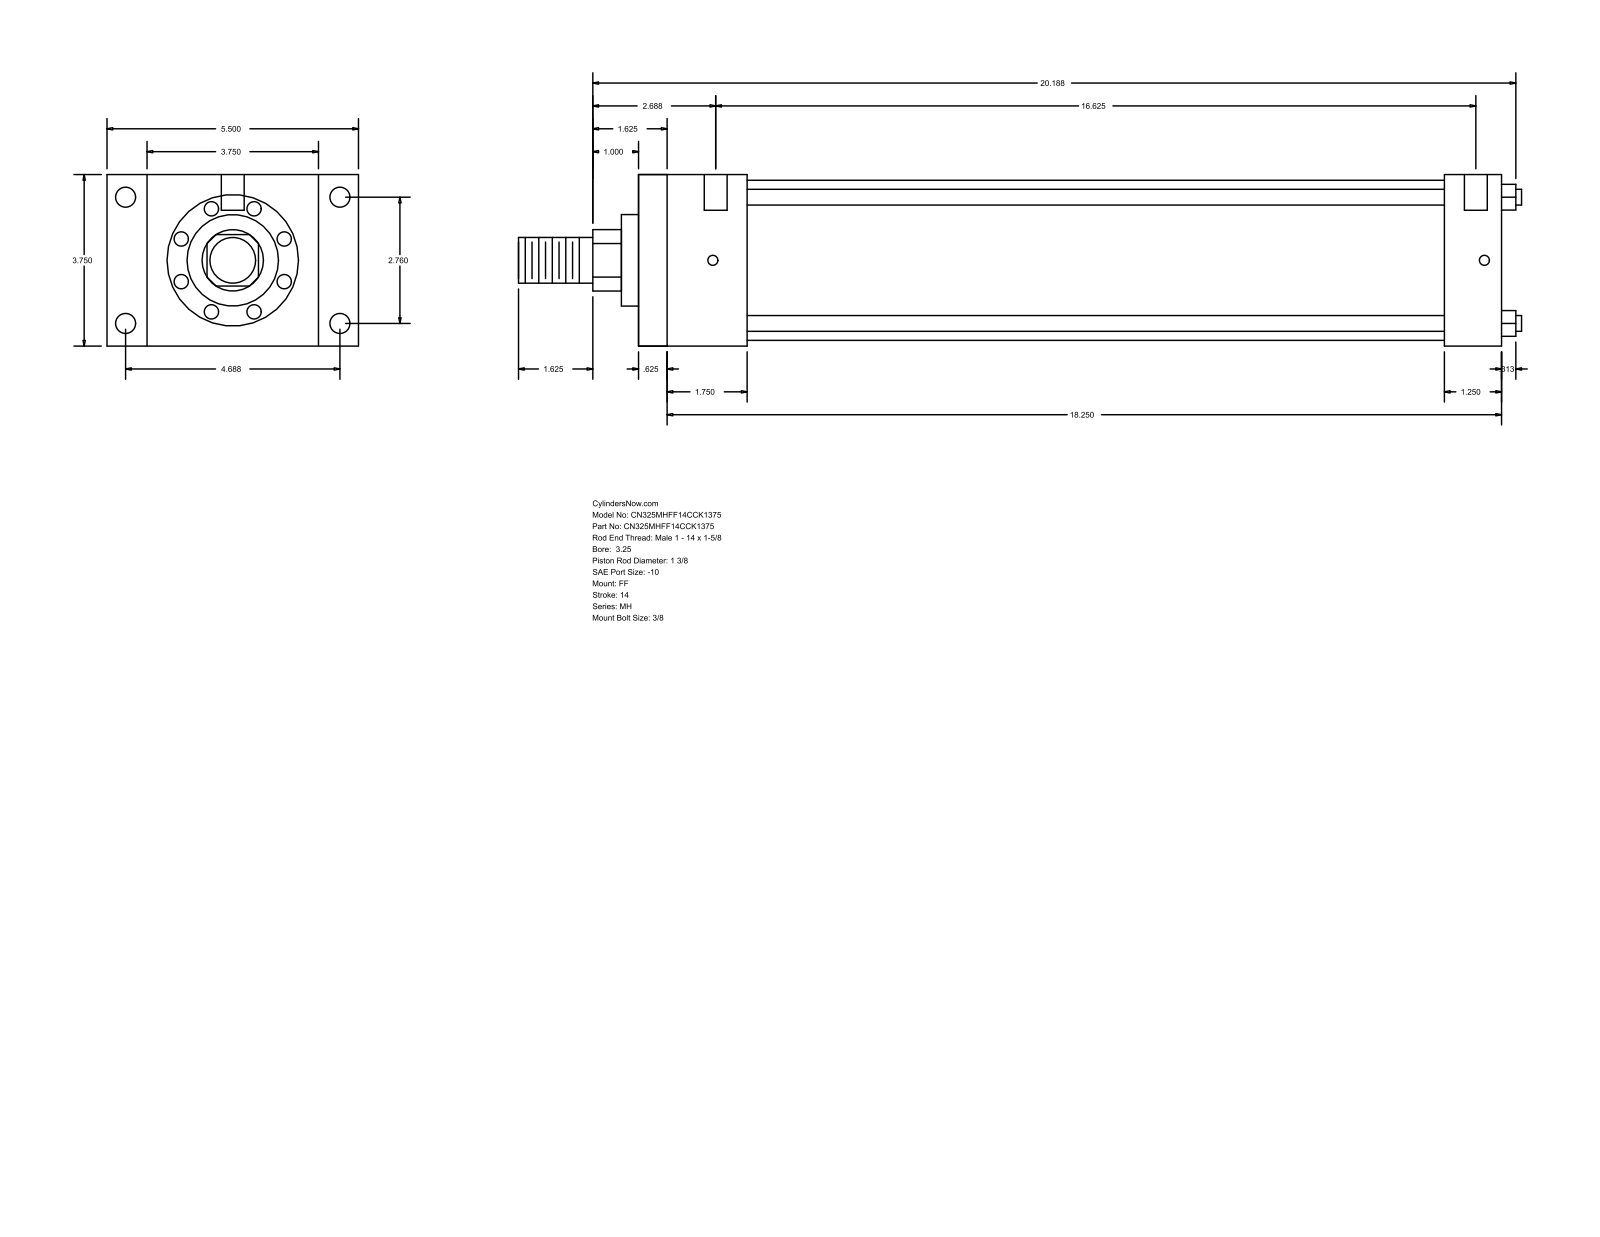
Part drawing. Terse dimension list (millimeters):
name: MH_FF__0325_1.375
written by: GSSL Pune (CONFIG_CONTROL_DESIGN)
unit: mm
bodies: 0 solids, 92 faces (64 planar, 28 cylindrical, 0 other)
size: 557.21 × 139.7 × 95.25
holes: 4× ⌀5.56, 4× ⌀11.13, 2× ⌀12.7
bosses: 4× ⌀8.76, 1× ⌀88.9, 1× ⌀50.8, 1× ⌀34.92, 1× ⌀25.4
rounds: 1× R17.06
face distances: 95.24, 479.42, 15.87, 463.55, 22.23, 117.47, 447.67, 431.8, 31.75, 60.32
hole spacings: 70.1, 119.06, 138.16, 428.63, 1.59, 4.76, 422.28, 423.87
